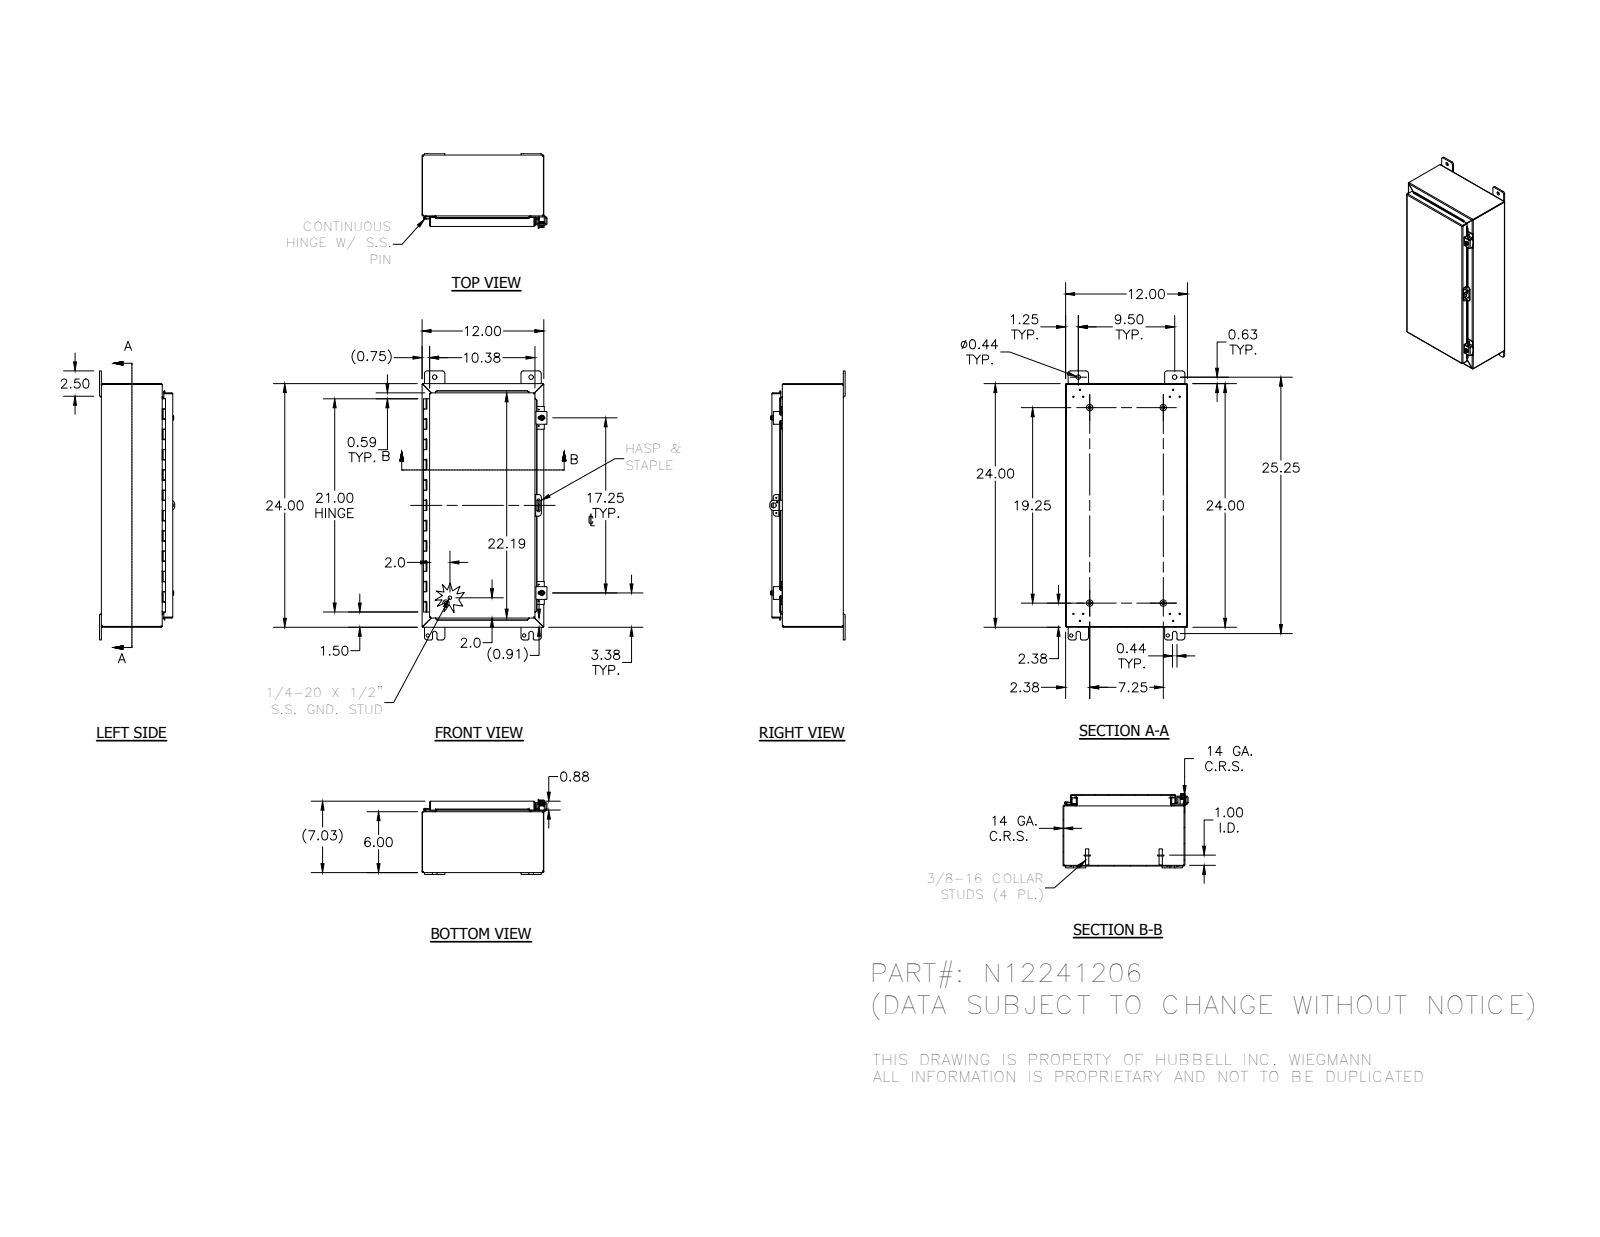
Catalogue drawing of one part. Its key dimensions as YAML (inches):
part_name: "N12241206; 34840; 38420; N12241206BKP (+8 more)"
step_written_by: "Autodesk Inventor 2012 (AUTOMOTIVE_DESIGN)"
units: inches
bodies: {solids: 27, faces: 982, planar: 533, cylindrical: 332, other: 117}
overall_size: [26.5, 12.311, 7.41]
volume: 99.56
surface_area: 2572
round_holes:
  - {diameter: 0.12, count: 12}
  - {diameter: 0.11, count: 7}
  - {diameter: 0.313, count: 4}
  - {diameter: 0.438, count: 4}
  - {diameter: 0.211, count: 2}
  - {diameter: 0.281, count: 2}
  - {diameter: 0.3, count: 2}
  - {diameter: 0.125, count: 1}
  - {diameter: 0.156, count: 1}
  - {diameter: 0.5, count: 1}
round_bosses_or_shafts:
  - {diameter: 0.625, count: 4}
  - {diameter: 0.33, count: 4}
  - {diameter: 0.25, count: 4}
  - {diameter: 0.52, count: 2}
  - {diameter: 0.5, count: 2}
  - {diameter: 0.35, count: 2}
  - {diameter: 0.115, count: 2}
  - {diameter: 0.337, count: 1}
partial_cylinders:
  - {radius: 0.03, count: 27}
  - {radius: 0.063, count: 25}
  - {radius: 0.125, count: 25}
  - {radius: 0.25, count: 25}
  - {radius: 0.031, count: 23}
  - {radius: 0.105, count: 23}
  - {radius: 0.07, count: 8}
  - {radius: 0.1, count: 4}
face_to_face_distances: [0.074, 6.959, 11.926, 6.885, 7.033, 5.926, 1.033, 23.926, 11.852, 12]
hole_center_spacings: [9.5, 0.759, 0.94, 0.969, 8.883, 9.85, 21.38, 21.402]
